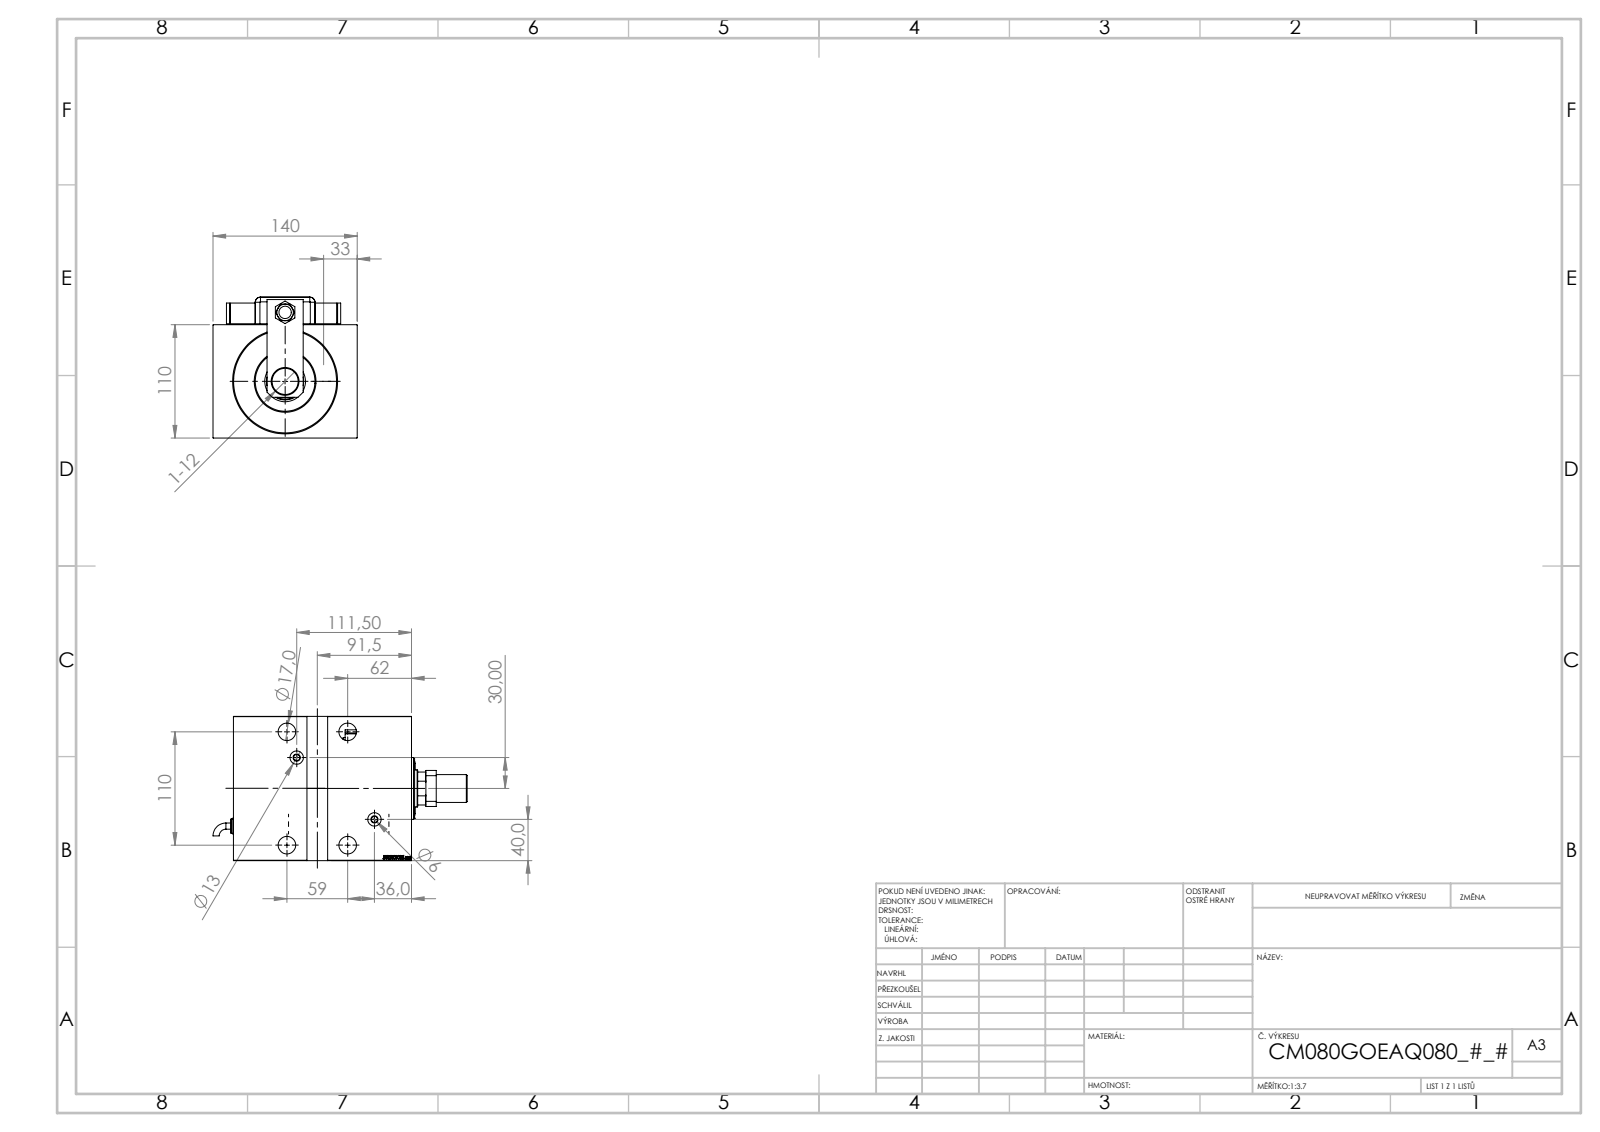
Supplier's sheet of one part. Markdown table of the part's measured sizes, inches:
| quantity | value |
| --- | --- |
| part name | V450CM_VC_G; NUT_D13; SWITCH Q; V450CM_MALE_METRIC (+7 more) |
| STEP written by | SolidWorks 2019 (CONFIG_CONTROL_DESIGN) |
| units | inches |
| bodies | 16 solids, 1294 faces (652 planar, 115 cylindrical, 527 other) |
| overall size | 9.715 × 5.512 × 5.386 |
| volume | 145.2 in³ |
| surface area | 497.3 in² |
| round holes (diameter × count) | 0.669 × 4, 0.984 × 4, 0.512 × 3, 0.157 × 2, 0.236 × 2, 0.315 × 2, 0.472 × 1, 0.551 × 1, 1.004 × 1, 1.063 × 1, 1.417 × 1, 1.555 × 1 |
| round bosses / shafts (diameter × count) | 0.787 × 3, 1.024 × 2, 0.63 × 2, 0.551 × 2, 0.276 × 2, 0.236 × 2, 2.362 × 1, 0.984 × 1 |
| partial cylindrical surfaces (radius × count) | 0.197 × 9, 0.394 × 1, 0.689 × 1 |
| main face-to-face distances | 4.331, 5.512, 0.118, 0.827, 6.811, 0.197, 5.984, 6.614, 5.787, 5.386 |
| hole center spacings | 2.323, 2.798, 3.352, 4.331, 4.825, 4.914, 5.167, 0.787 |
